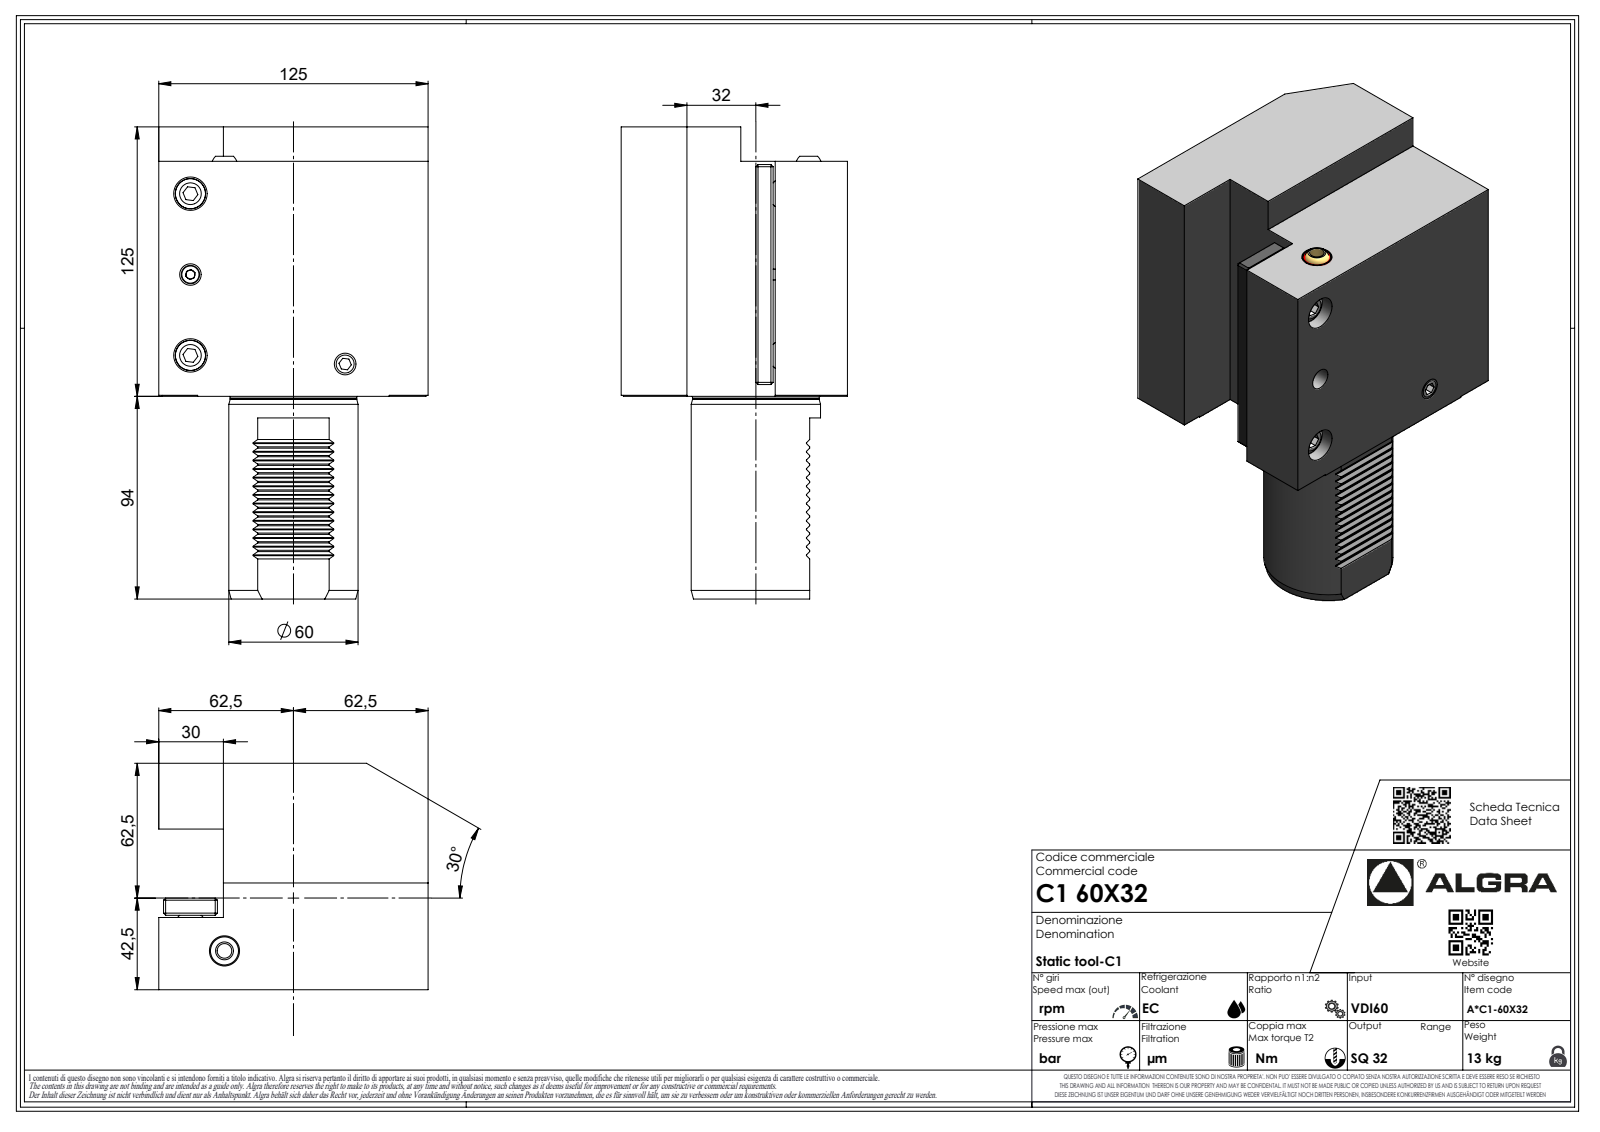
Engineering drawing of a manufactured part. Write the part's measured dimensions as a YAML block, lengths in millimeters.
part_name: "C160X32"
step_written_by: "SolidWorks 2023 (AUTOMOTIVE_DESIGN)"
units: millimeters
bodies: {solids: 1, faces: 322, planar: 217, cylindrical: 45, other: 60}
overall_size: [219, 125, 105]
volume: 1640000
surface_area: 108999
round_holes:
  - {diameter: 2.1, count: 1}
round_bosses_or_shafts:
  - {diameter: 60, count: 1}
  - {diameter: 58.7, count: 1}
  - {diameter: 6.37, count: 1}
  - {diameter: 5, count: 1}
  - {diameter: 1.7, count: 1}
partial_cylinders:
  - {radius: 0.3, count: 14}
  - {radius: 0.33, count: 7}
  - {radius: 0.52, count: 7}
  - {radius: 3.7, count: 7}
  - {radius: 0.21, count: 1}
  - {radius: 61.5, count: 1}
face_to_face_distances: [125, 105, 16, 109, 95, 30, 30.5, 74.5, 32, 25]
